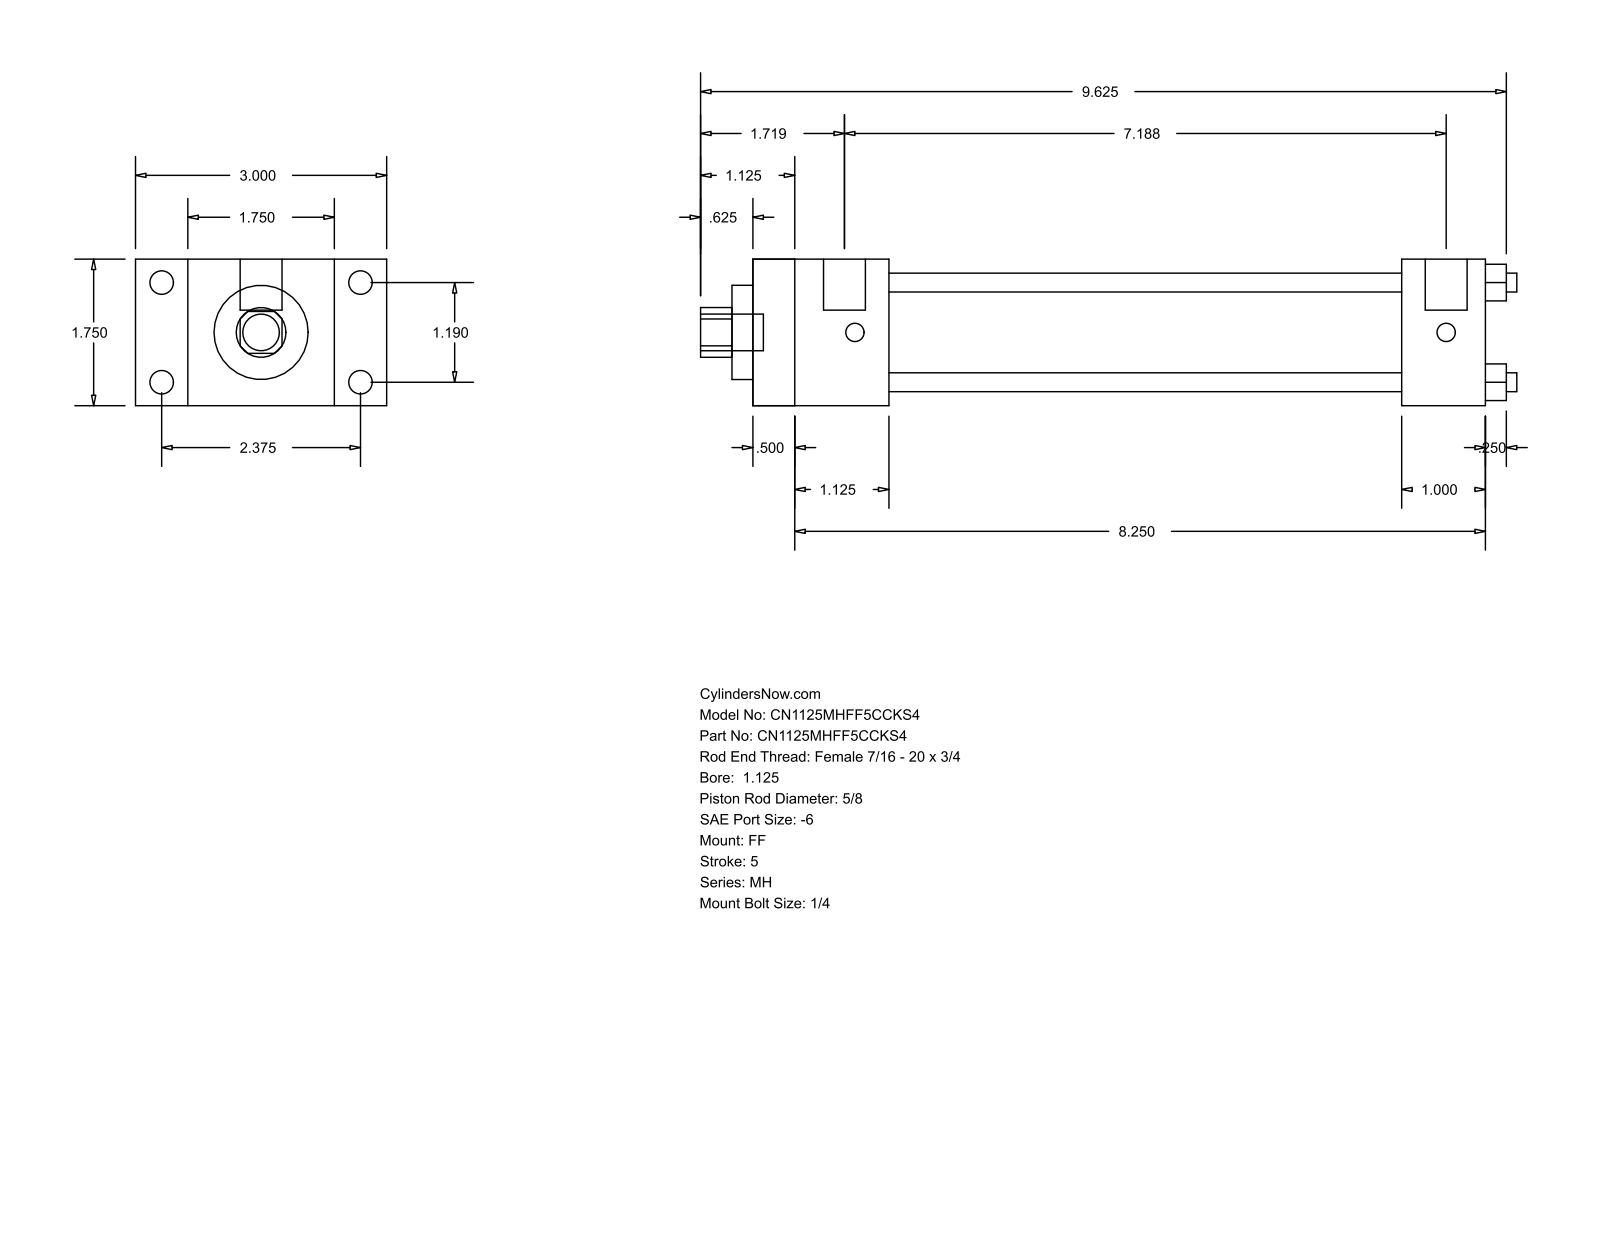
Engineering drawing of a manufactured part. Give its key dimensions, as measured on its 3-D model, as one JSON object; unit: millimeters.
{"part_name": "MH_FF__0112_0.625", "step_written_by": "GSSL Pune (CONFIG_CONTROL_DESIGN)", "units": "millimeters", "bodies": {"solids": 0, "faces": 92, "planar": 64, "cylindrical": 28, "other": 0}, "overall_size": [247.65, 76.2, 44.45], "round_holes": [[5.71, 4], [15.88, 1], [28.57, 1], [34.92, 1]], "round_bosses_or_shafts": [[7.14, 4], [5.56, 4], [12.7, 2], [11.11, 1]], "partial_cylinders_radius": [[7.54, 1]], "face_to_face_distances": [44.46, 222.24, 12.69, 209.55, 15.87, 60.33, 28.58, 41.27, 196.84, 184.15], "hole_center_spacings": [21.37, 30.22, 42.74]}
